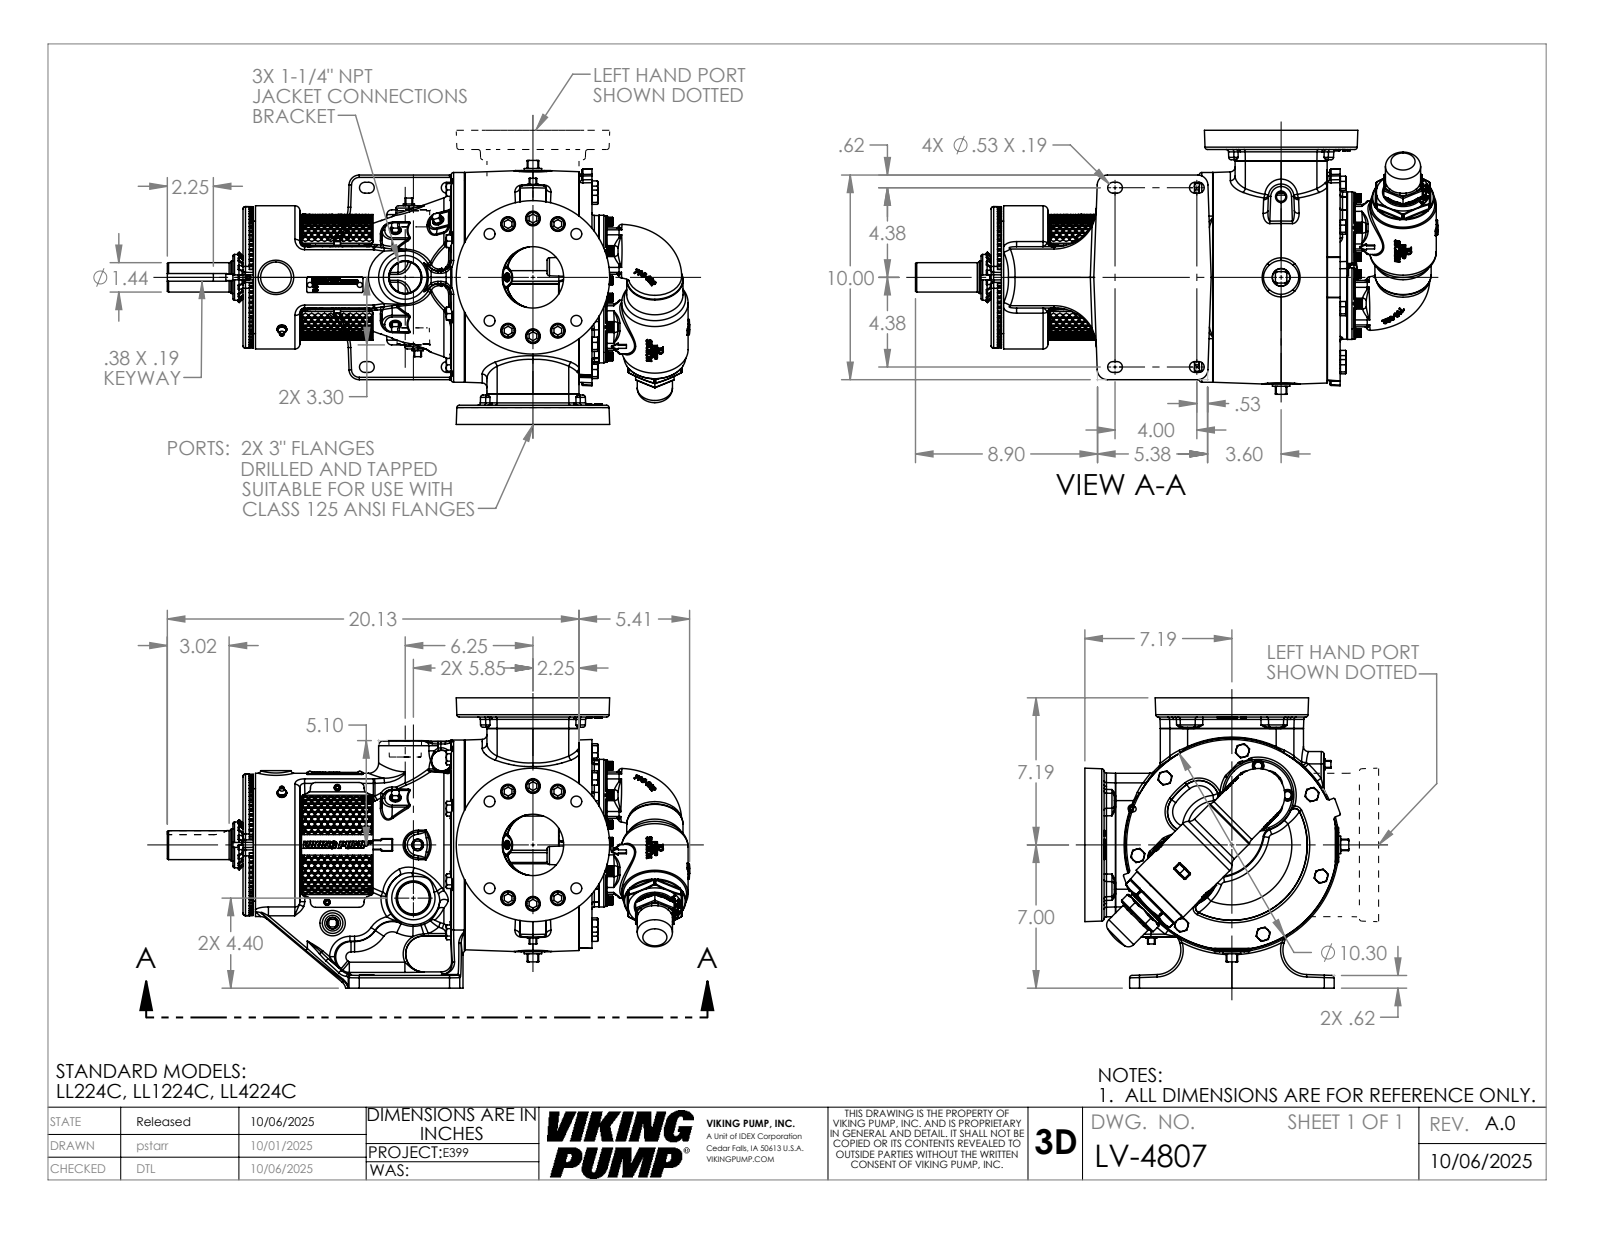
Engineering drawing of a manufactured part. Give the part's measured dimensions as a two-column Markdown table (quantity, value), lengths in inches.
| quantity | value |
| --- | --- |
| part name | LV-4807 |
| STEP written by | SolidWorks 2024 (AUTOMOTIVE_DESIGN) |
| units | inches |
| bodies | 1 solid, 6460 faces (2041 planar, 1168 cylindrical, 3251 other) |
| overall size | 25.533 × 14.187 × 12.902 |
| volume | 1 155 in³ |
| surface area | 1 507 in² |
| round holes (diameter × count) | 0.719 × 12, 0.25 × 9, 0.531 × 8, 1.094 × 8, 0.199 × 6, 0.159 × 3, 0.266 × 2, 0.313 × 2, 3 × 2, 0.453 × 1, 1.552 × 1, 1.578 × 1 |
| round bosses / shafts (diameter × count) | 0.66 × 12, 0.625 × 10, 0.563 × 8, 0.625 × 5, 0.312 × 3, 0.19 × 3, 3.5 × 2, 10.25 × 1 |
| partial cylindrical surfaces (radius × count) | 0.063 × 109, 0.069 × 74, 0.01 × 66, 0.12 × 64, 0.03 × 36, 0.5 × 26, 0.06 × 16, 0.24 × 16 |
| main face-to-face distances | 14.187, 10.77, 3.54, 14.31, 0.5, 0.94, 2.25, 1.382, 0.442, 2.14 |
| hole center spacings | 3, 4.243, 2.875, 1.375, 1.028, 1.244, 2.18, 2.251 |
